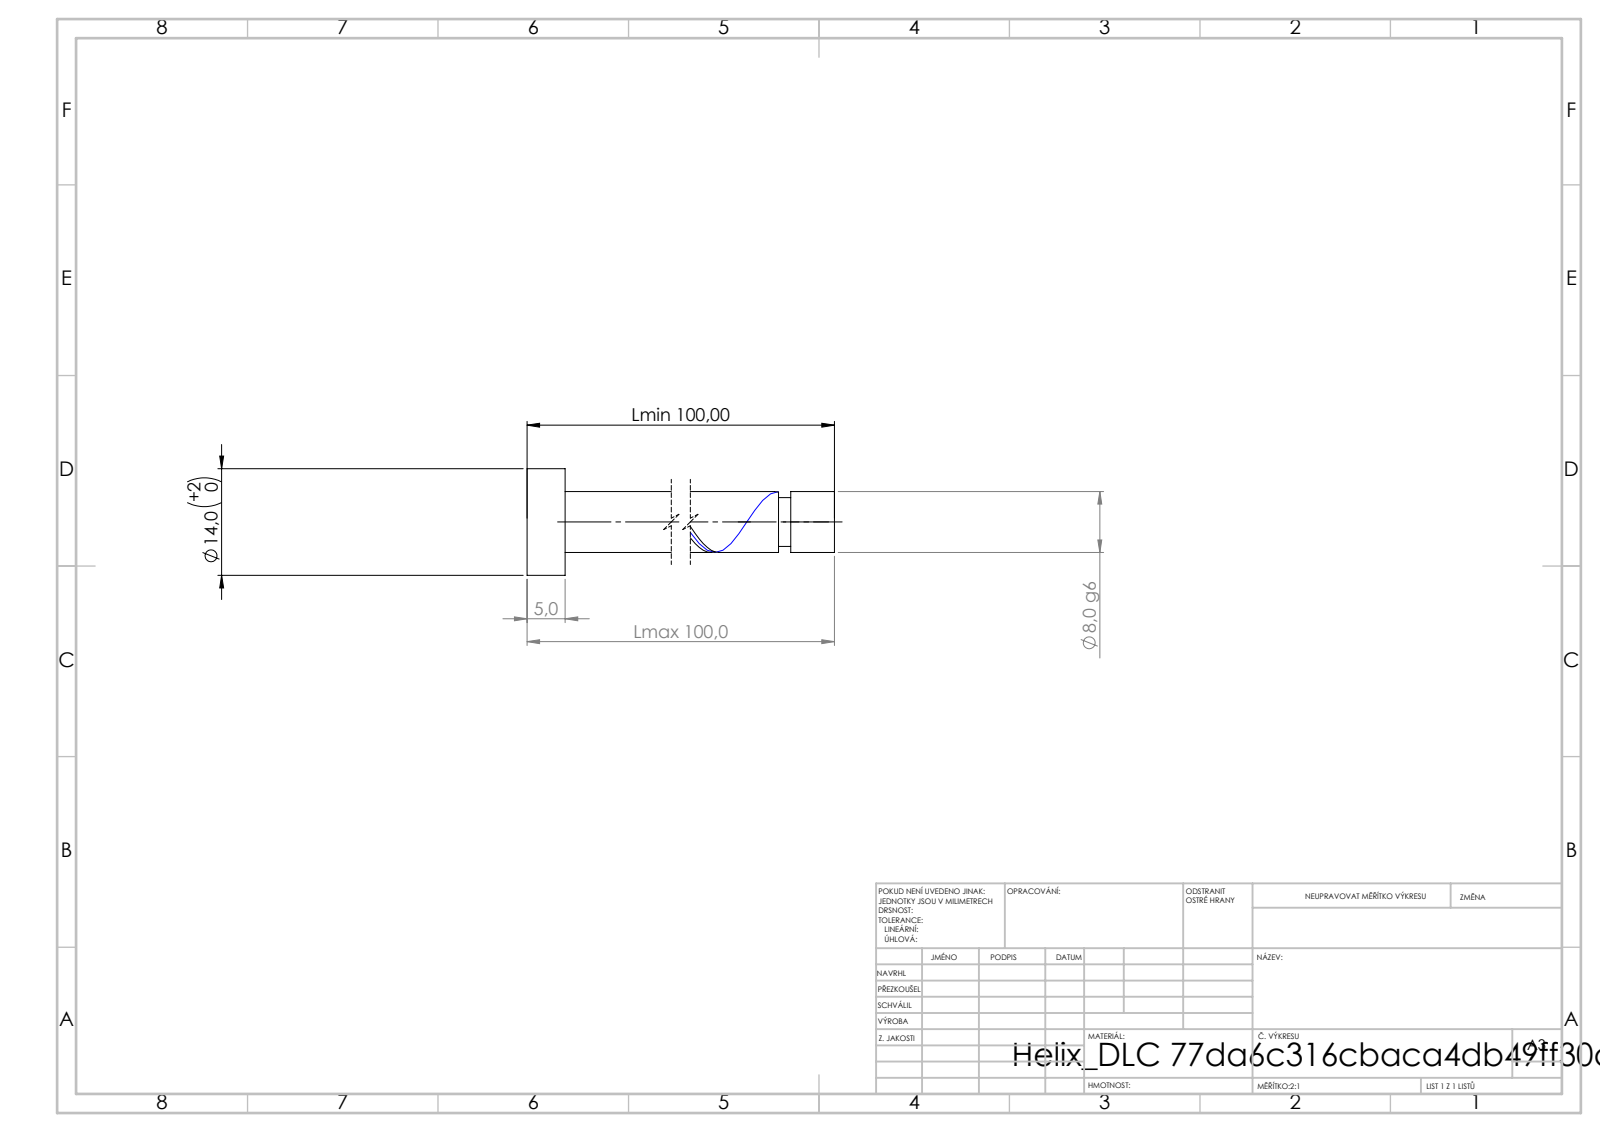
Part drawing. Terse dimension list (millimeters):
written by: SolidWorks 2019 (CONFIG_CONTROL_DESIGN)
unit: mm
bodies: 1 solid, 21 faces (6 planar, 14 cylindrical, 1 other)
size: 100 × 14 × 14
volume: 5 468 mm³; area: 3 029 mm²
bosses: 1× ⌀14, 1× ⌀8, 1× ⌀6.4
face distances: 5, 100, 95, 94.27, 89.27, 5.73, 92.67, 87.67, 1.6, 7.33
